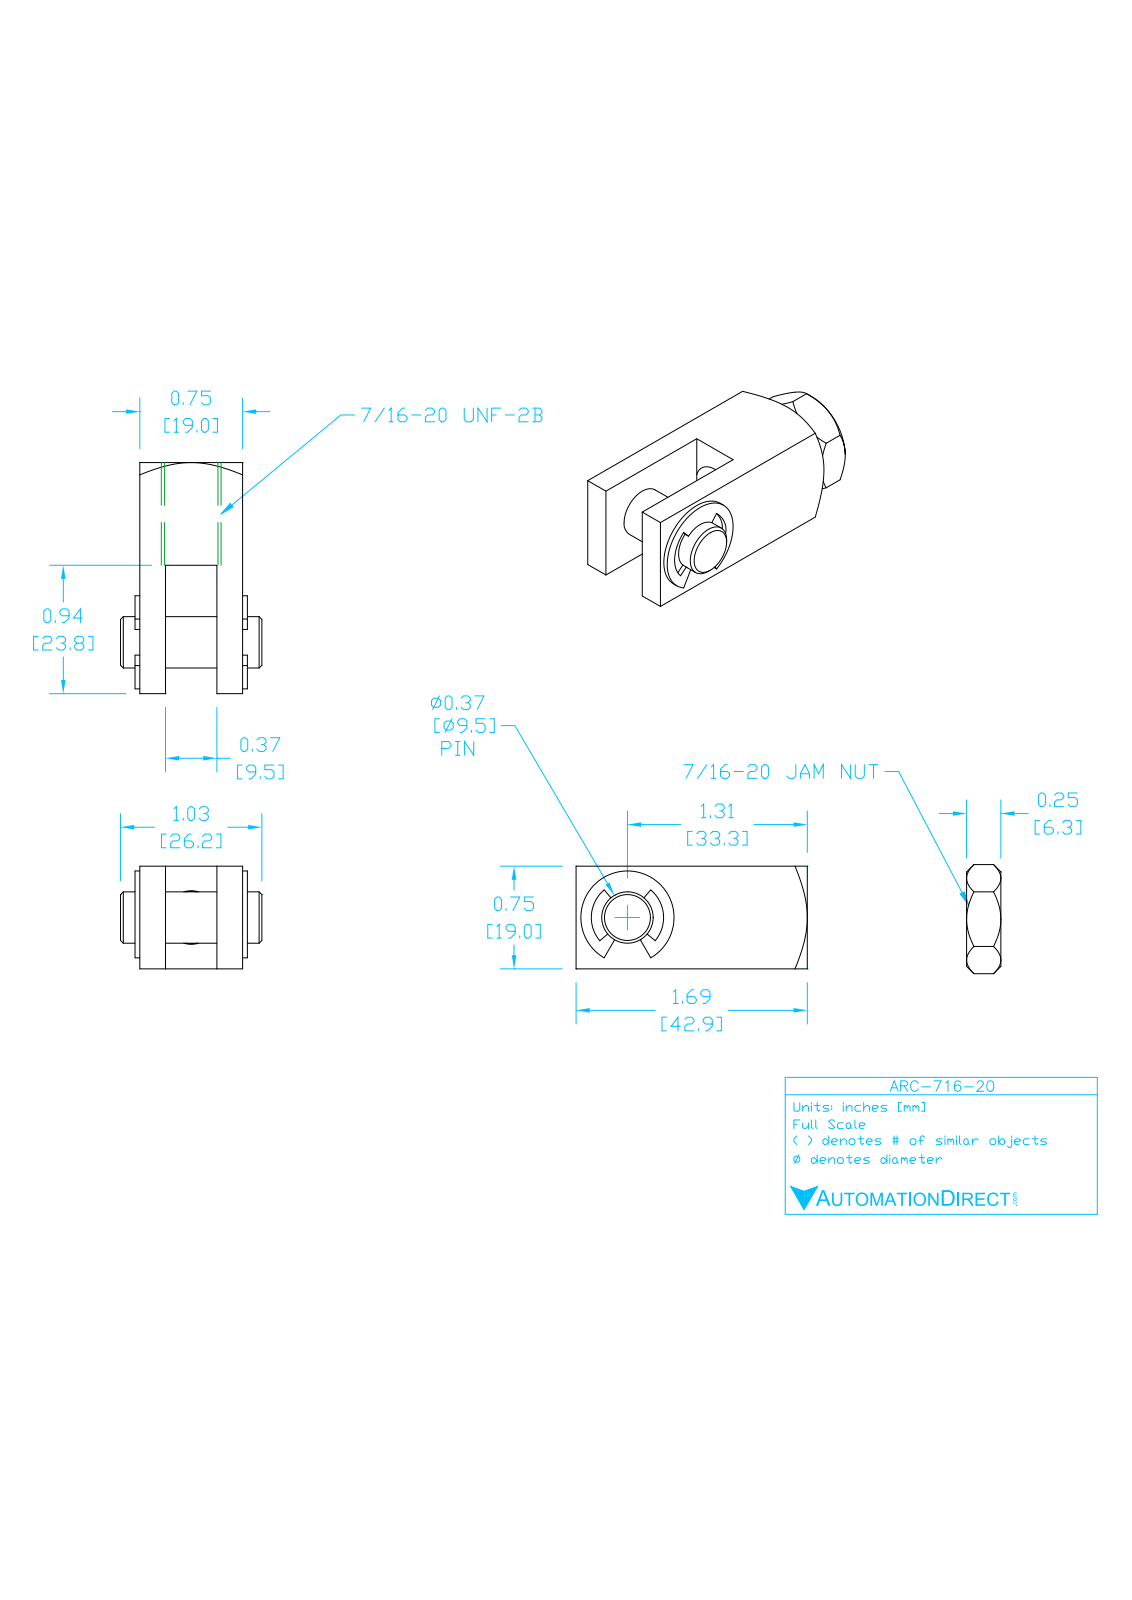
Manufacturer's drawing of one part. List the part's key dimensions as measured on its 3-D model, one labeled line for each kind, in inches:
Part name (STEP PRODUCT): ARC-716-20
STEP written by: SolidWorks 2017 (AUTOMOTIVE_DESIGN)
Units: inches
Bodies: 5 solids, 136 faces (44 planar, 58 cylindrical, 34 other)
Overall size (bounding box): 1.938 × 1.031 × 0.797
Volume: 0.749 in³ · Surface area: 11.7 in²
Round holes (diameter × count): ⌀0.372 ×1, ⌀0.383 ×1, ⌀0.391 ×1
Round bosses / shafts (diameter × count): ⌀0.377 ×1, ⌀0.304 ×1
Partial cylindrical surfaces — rounded edges, fillets, slot ends (radius × count): R0.031 ×6, R0.035 ×4, R0.053 ×2, R0.152 ×1, R0.153 ×1, R0.264 ×1, R0.375 ×1
Main face-to-face distances: 0.75, 0.181, 0.569, 0.387, 0.796, 0.041, 0.222, 0.61, 0.791, 0.186
